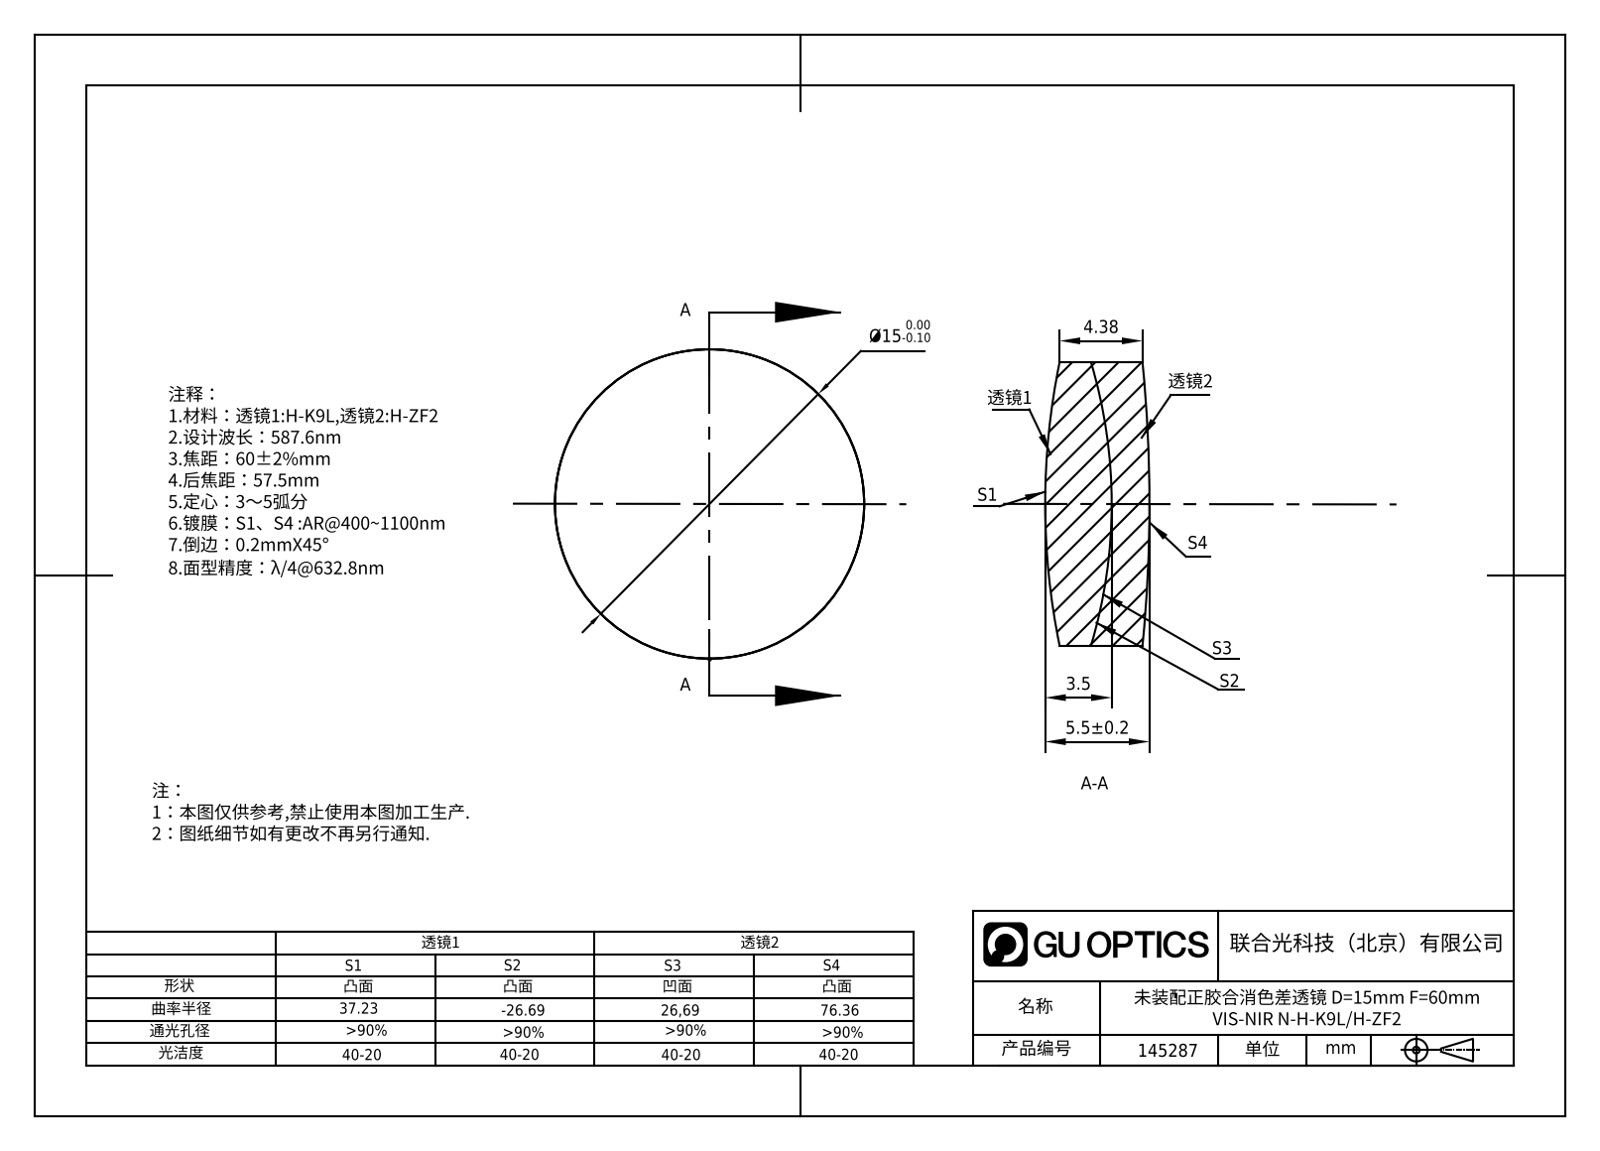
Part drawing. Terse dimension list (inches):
name: 145287
written by: SolidWorks 2020 (CONFIG_CONTROL_DESIGN)
unit: in
bodies: 2 solids, 12 faces (0 planar, 4 cylindrical, 8 other)
size: 0.591 × 0.591 × 0.217
volume: 0.053 in³; area: 1.43 in²
bosses: 1× ⌀0.591
